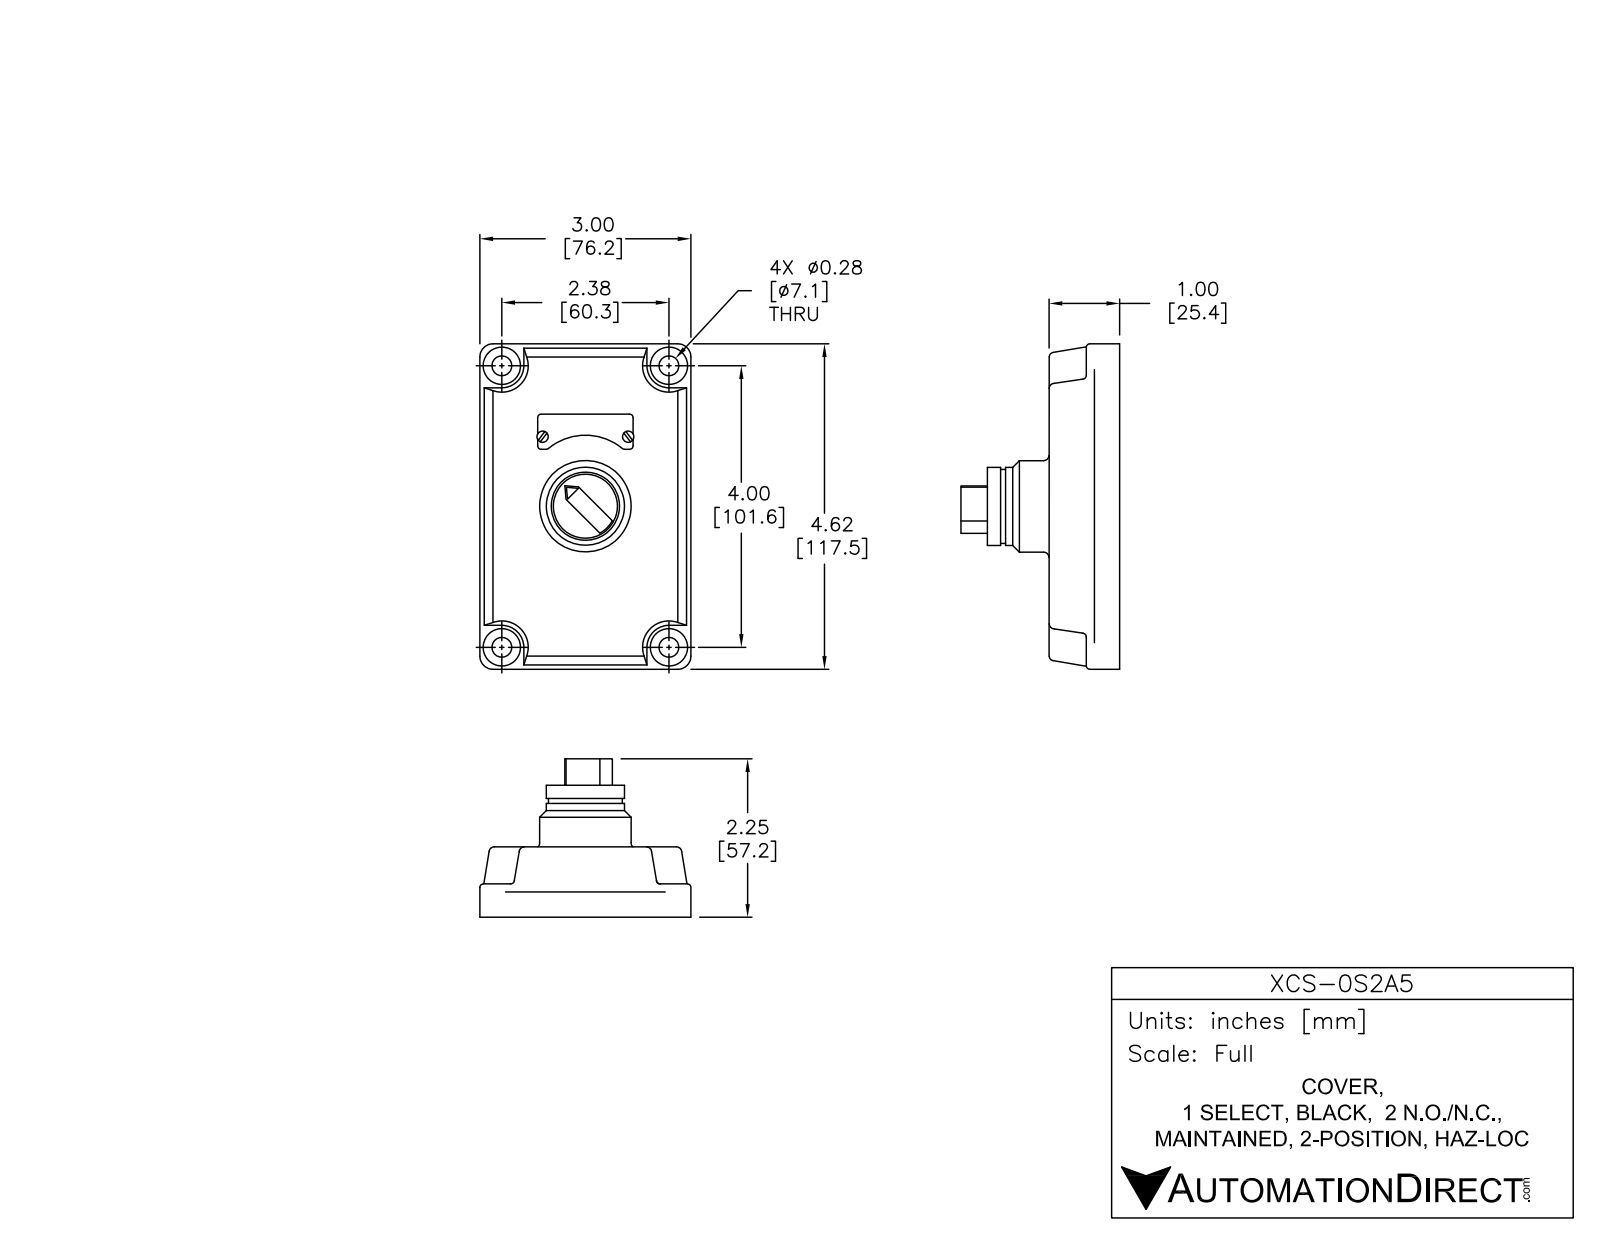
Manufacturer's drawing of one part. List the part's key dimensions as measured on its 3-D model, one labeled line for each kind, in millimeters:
Part name (STEP PRODUCT): XCS-0S2A5
STEP written by: SolidWorks 2015 (AUTOMOTIVE_DESIGN)
Units: millimetres
Bodies: 11 solids, 508 faces (211 planar, 166 cylindrical, 131 other)
Overall size (bounding box): 117.6 × 95.04 × 78.74
Volume: 237 390 mm³ · Surface area: 60 752 mm²
Round holes (diameter × count): ⌀6.86 ×4, ⌀14.5 ×1, ⌀24.64 ×1
Round bosses / shafts (diameter × count): ⌀3.3 ×8, ⌀11.6 ×4, ⌀6.35 ×4, ⌀33.02 ×1, ⌀28.19 ×1, ⌀26.67 ×1, ⌀24 ×1, ⌀23.11 ×1
Partial cylindrical surfaces — rounded edges, fillets, slot ends (radius × count): R0.25 ×28, R1.27 ×10, R0.51 ×8, R1.4 ×8, R2.54 ×4, R3.5 ×4, R9.65 ×4, R15.24 ×4
Main face-to-face distances: 13.34, 12.7, 26.04, 0.63, 12.3, 25, 38.34, 7.5, 38.97, 26.67
Hole centre spacings: 59.11, 60.46, 101.6, 118.23
